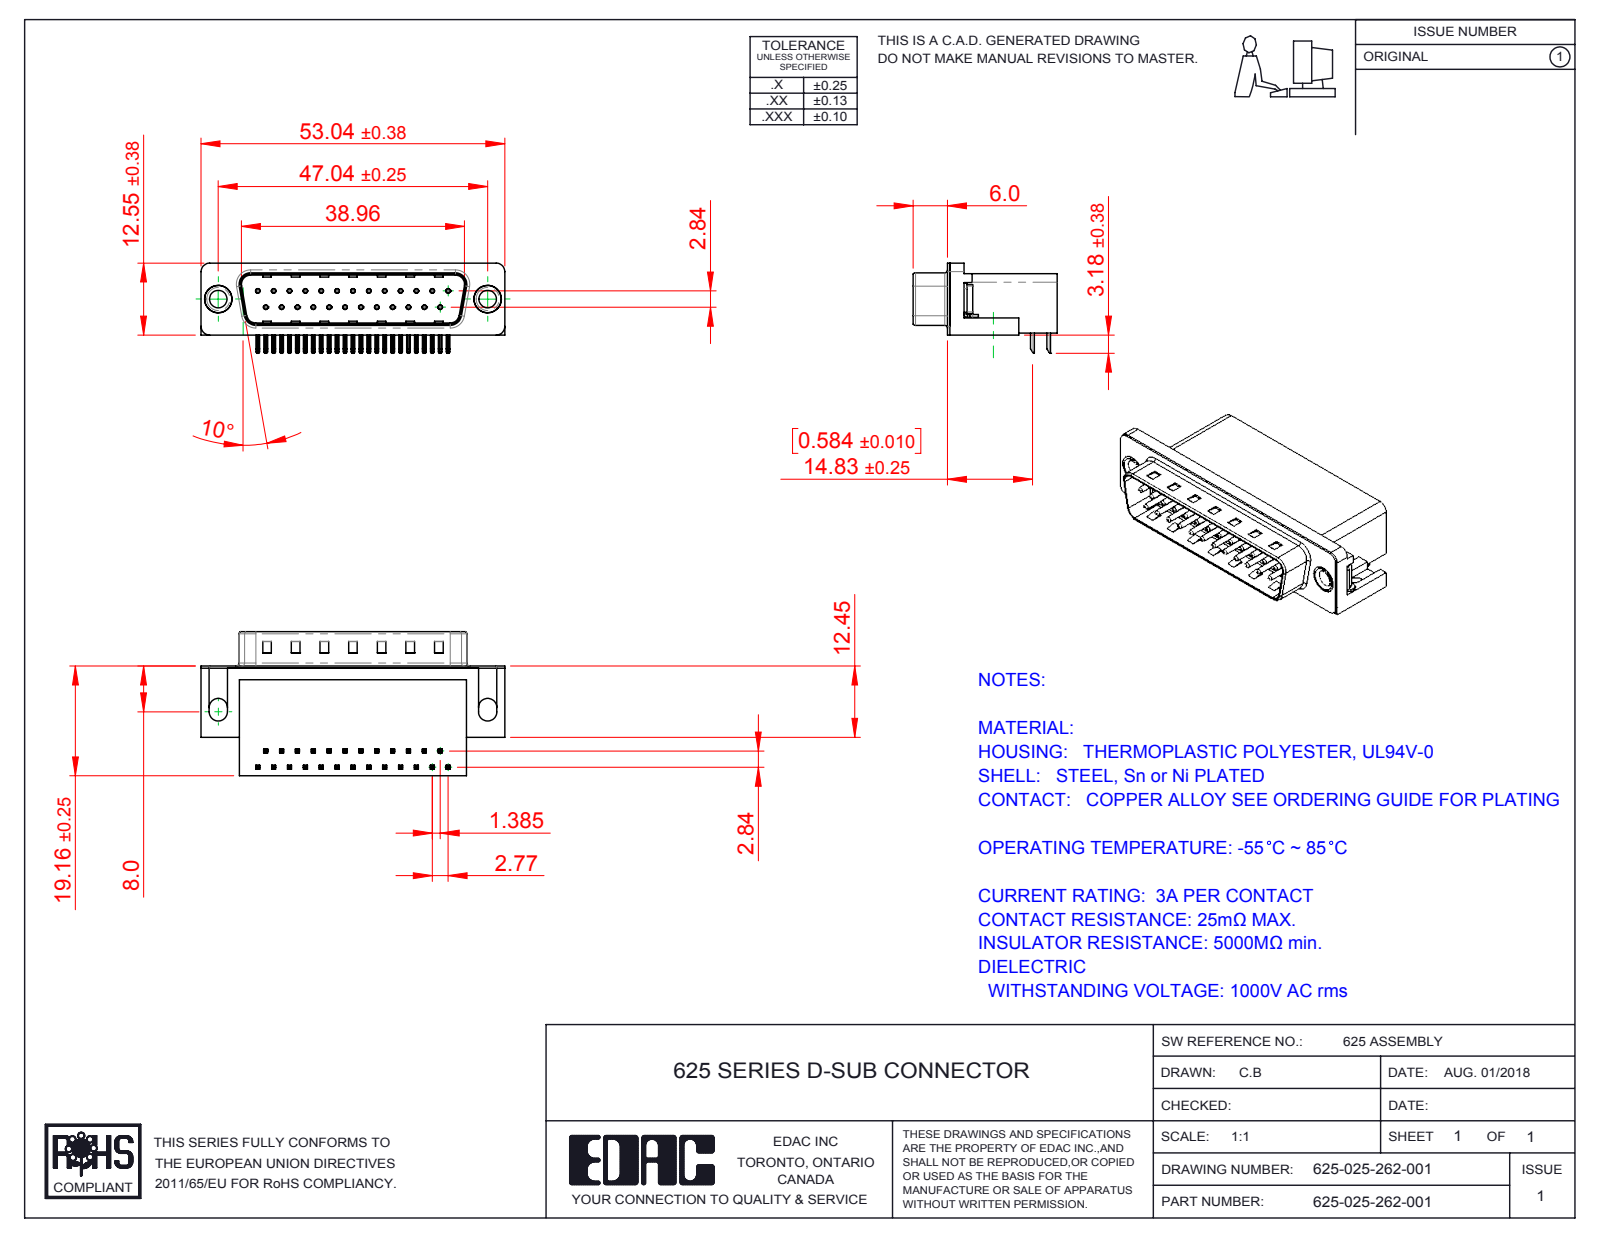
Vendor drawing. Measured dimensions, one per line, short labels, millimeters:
name: 625-025-262-001; 625 Contact Bottom; 625 Shell_25 Socket; 625 Thru Hole Rivet (+3 more)
written by: SolidWorks 2016 (CONFIG_CONTROL_DESIGN)
unit: mm
bodies: 31 solids, 2223 faces (1407 planar, 639 cylindrical, 177 other)
size: 53.04 × 25.16 × 15.73
volume: 9 125 mm³; area: 8 704 mm²
holes: 25× ⌀0.35, 25× ⌀0.8, 2× ⌀3.05, 2× ⌀4, 2× ⌀4.8, 2× ⌀5
bosses: 25× ⌀0.75, 2× ⌀4.9, 2× ⌀4.75, 2× ⌀3.85
rounds: 108× R0.25, 50× R0.12, 16× R1, 9× R0.5, 8× R1.6, 7× R1.5, 4× R0.9, 4× R2
face distances: 0.4, 10.35, 18.76, 2.1, 8.76, 10.46, 10.86, 1.7, 19.16, 10.11
hole spacings: 3.16, 2.77, 11.08, 5.54, 8.31, 5.03, 13.85, 7.48
